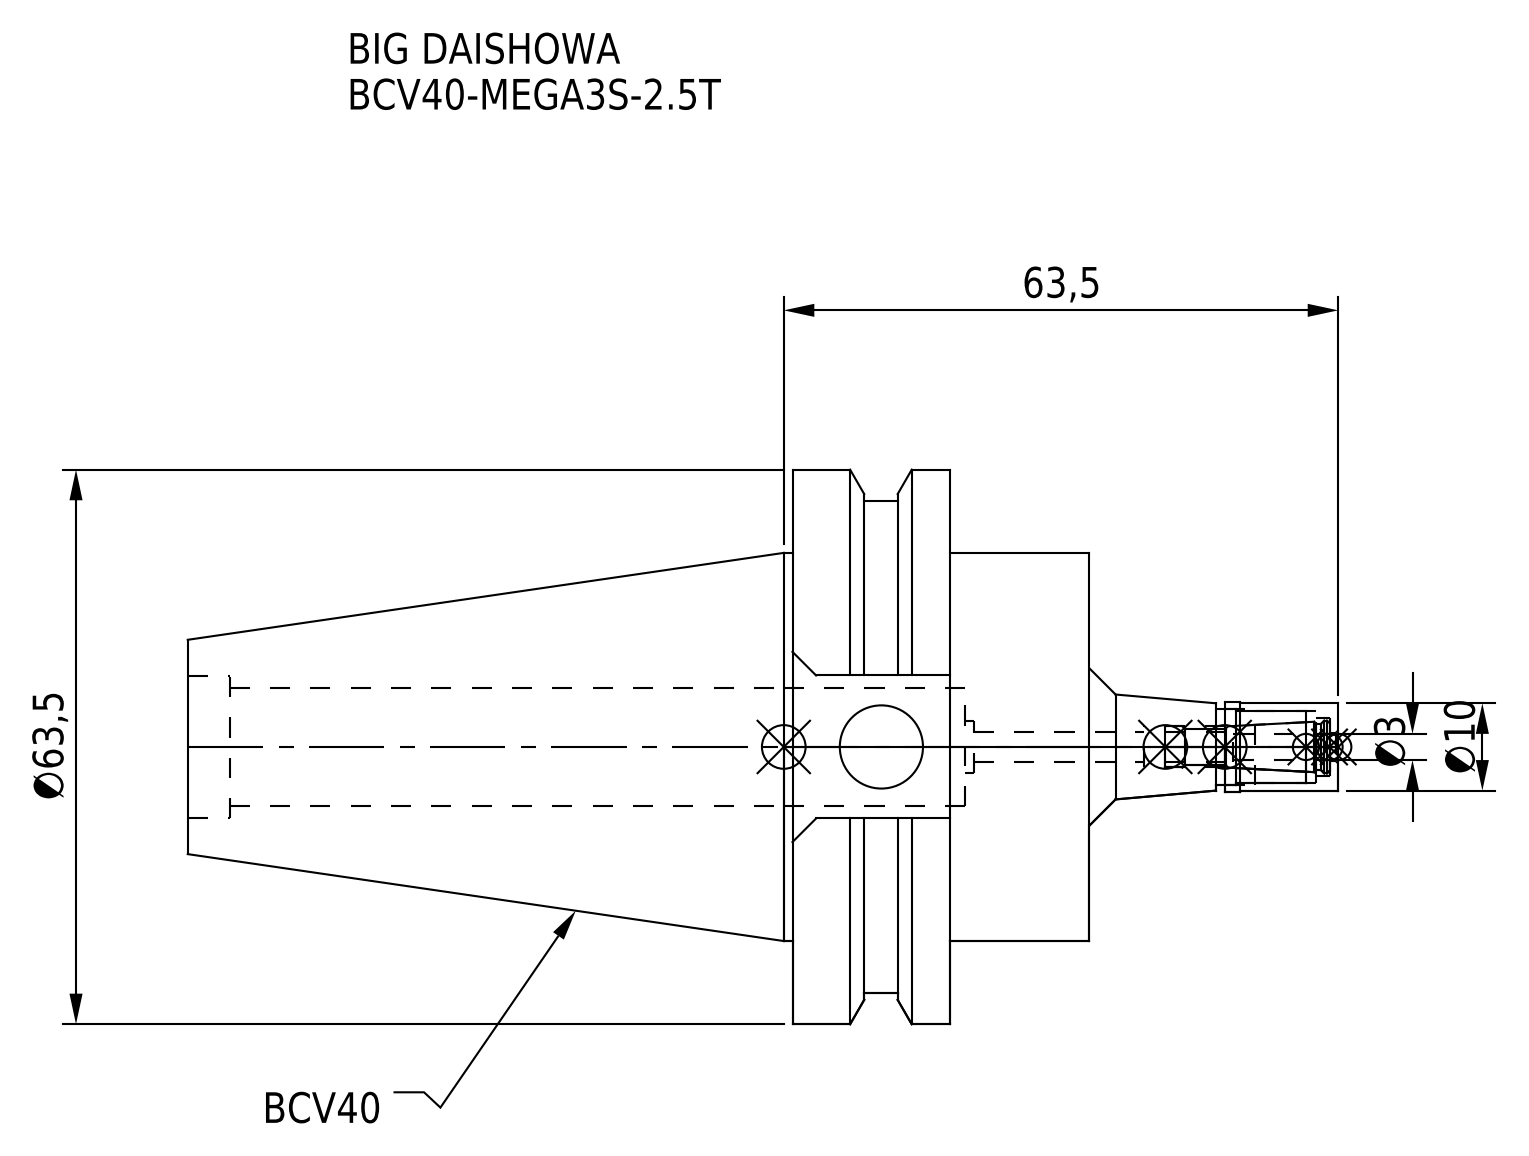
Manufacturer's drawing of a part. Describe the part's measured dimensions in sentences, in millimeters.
The part is named "BCV40-MEGA3S-2_5T_1.stp; BCV40-MEGA3S-2_5T-030-FreeParts; BCV40MS03025T-030_ASM.stp; MGN3S_1.stp (+3 more)". Its 3-D file was written by "SolidWorks 2019 (CONFIG_CONTROL_DESIGN)". It is 2 solids with 86 faces: 32 planar, 40 cylindrical and 14 other. Overall it measures 131.75 by 63.5 by 61.35 millimeters. Its volume is 130 344 cubic millimeters and its surface area 25 101 square millimeters. Round holes: 1 of diameter 3.3, 1 of diameter 3.4, 1 of diameter 4.7, 1 of diameter 6, 1 of diameter 6.6, 1 of diameter 8.2, 1 of diameter 8.7, 1 of diameter 9.53, 1 of diameter 13.6, 1 of diameter 16.32. Round bosses or shafts: 1 of diameter 63.5, 1 of diameter 56.36, 1 of diameter 44.45, 1 of diameter 10.3, 1 of diameter 10. The main face-to-face distances are 15.95, 34, 18.05, 103.25, 87.3, 69.25, 47.55, 16.38, 1.7, 14.25.
